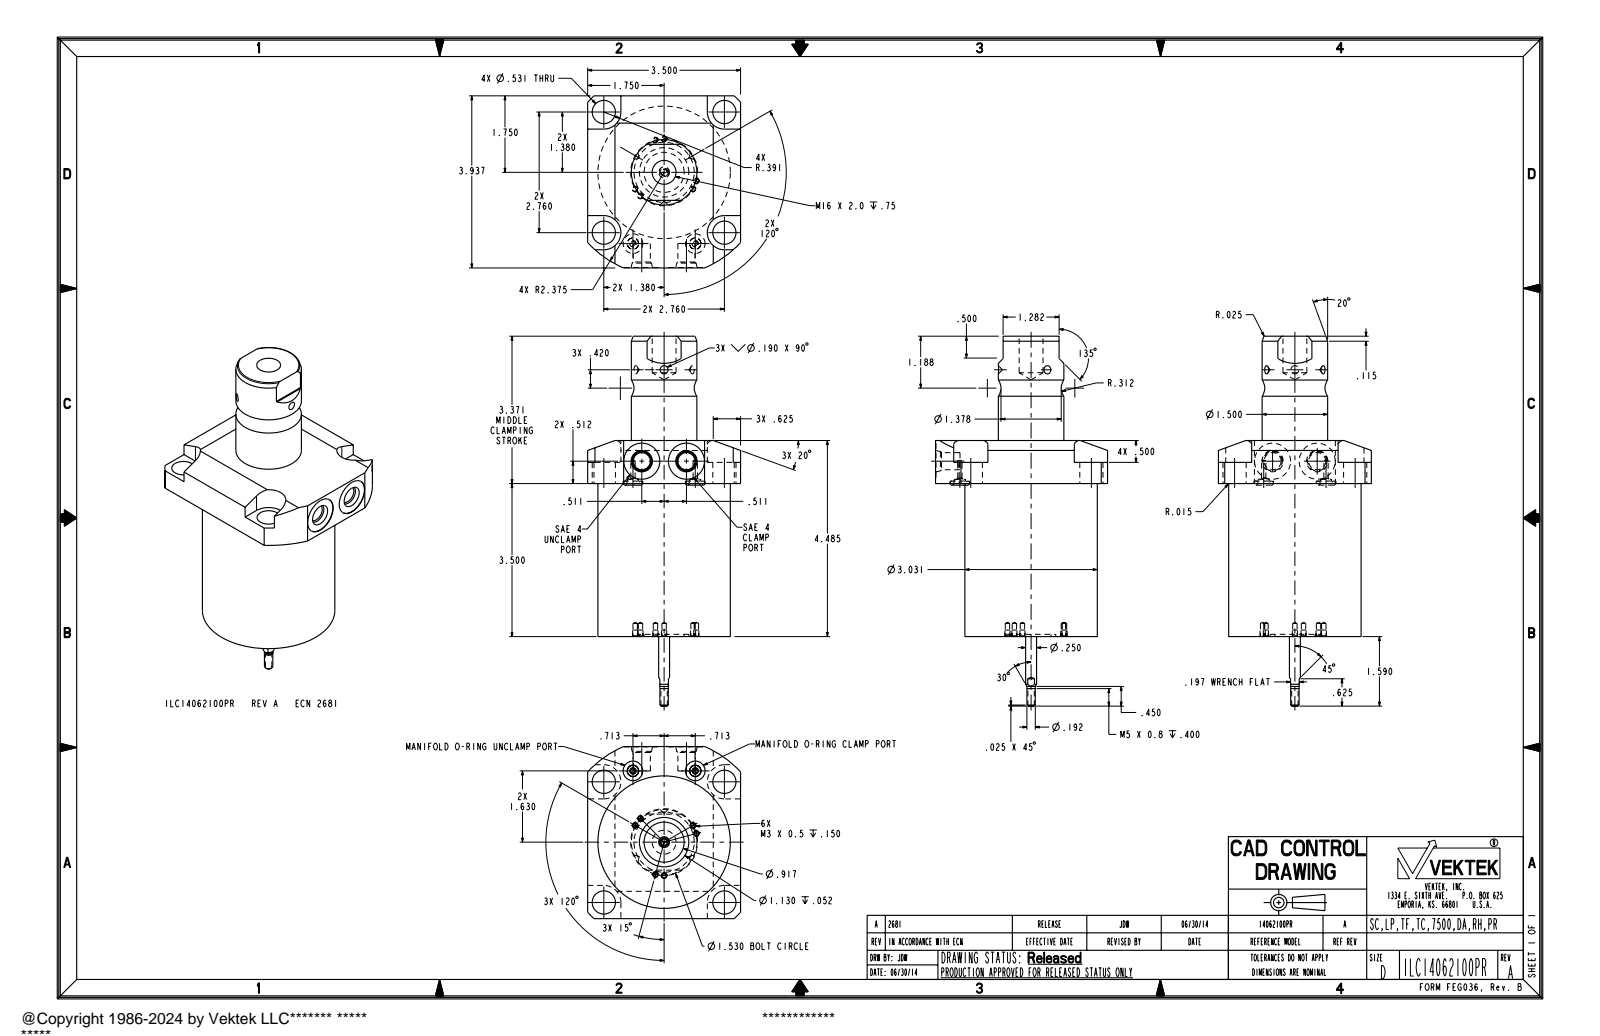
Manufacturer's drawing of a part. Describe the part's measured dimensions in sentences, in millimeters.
The part is named "ILC14062100PR". Its 3-D file was written by "PRO/ENGINEER BY PARAMETRIC TECHNOLOGY CORPORATION, 2013320 (AUTOMOTIVE_DESIGN)". It is 3 solids with 197 faces: 53 planar, 80 cylindrical and 64 other. Overall it measures 214.9 by 100 by 88.9 millimeters. Its volume is 659 100 cubic millimeters and its surface area 59 260 square millimeters. Round holes: 6 of diameter 2.5, 4 of diameter 13.5, 2 of diameter 2.5, 2 of diameter 6.5, 2 of diameter 10, 2 of diameter 11.4, 2 of diameter 21, 1 of diameter 13.9, 1 of diameter 28.7. Round bosses or shafts: 6 of diameter 3, 1 of diameter 77, 1 of diameter 38.1, 1 of diameter 23.3, 1 of diameter 6.4, 1 of diameter 4.9, 1 of diameter 3.7. Partial cylindrical surfaces (rounded edges, fillets, slot ends): 4 of radius 9.9, 2 of radius 0.8, 1 of radius 60.3. The main face-to-face distances are 88.9, 113.9, 25, 174.5, 85.6, 60.6, 101.2, 12.3, 12.7, 73.3. The hole center spacings are 33.7, 19.4, 49.6, 70.1, 5.1, 18.1, 19.4, 30.8.
